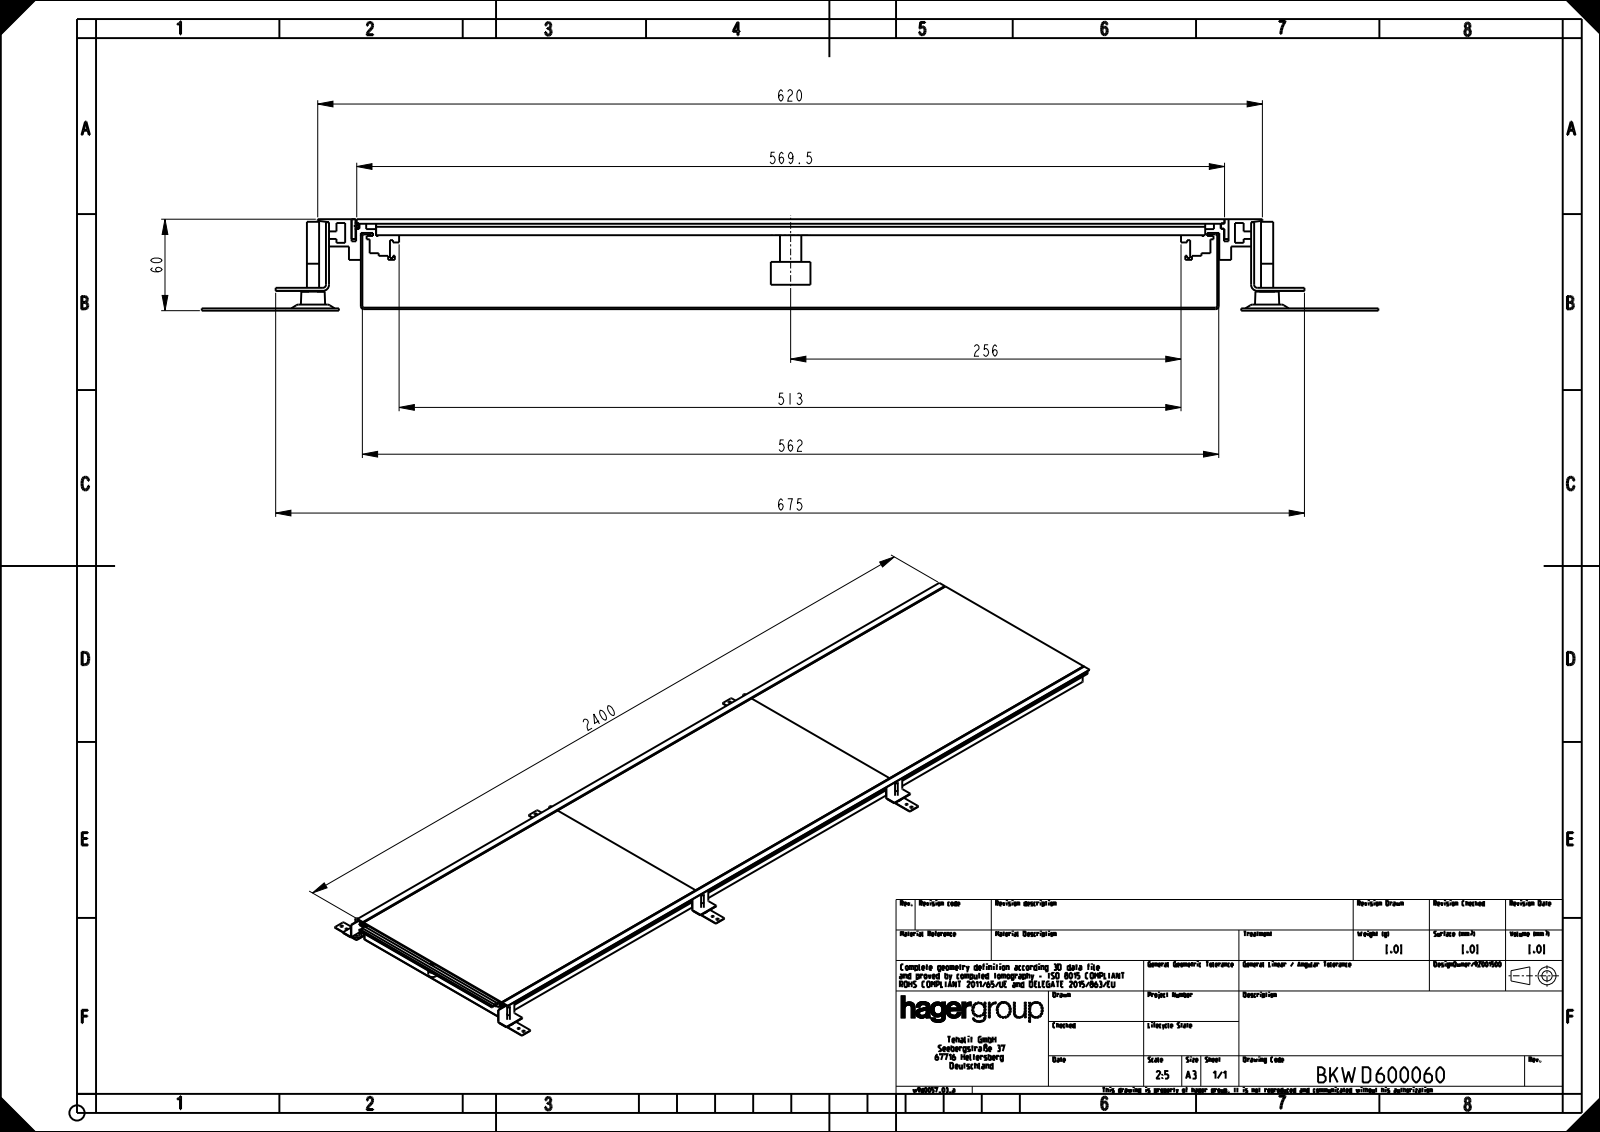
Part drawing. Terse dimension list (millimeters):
name: U05644KUN; U05650KUN; U05647KUN; U05826KUN (+8 more)
written by: CREO PARAMETRIC BY PTC INC, 2020281 (AUTOMOTIVE_DESIGN)
unit: mm
bodies: 61 solids, 1036 faces (606 planar, 358 cylindrical, 72 other)
size: 2432.5 × 772.13 × 60
volume: 10 260 000 mm³; area: 8 491 000 mm²
holes: 15× ⌀7, 9× ⌀8, 9× ⌀10, 6× ⌀6, 6× ⌀8.5, 6× ⌀11.5, 6× ⌀17.5, 6× ⌀23
bosses: 9× ⌀26, 9× ⌀14, 9× ⌀11.9, 6× ⌀20, 6× ⌀8
rounds: 96× R2, 24× R3, 20× R0.5, 4× R1, 2× R4
face distances: 1, 3, 56, 59, 55, 58, 7.5, 6.5, 48.5, 47.5
hole spacings: 800, 1600, 800.25, 801.1, 802.4, 1042.3, 1055.24, 1083.09
